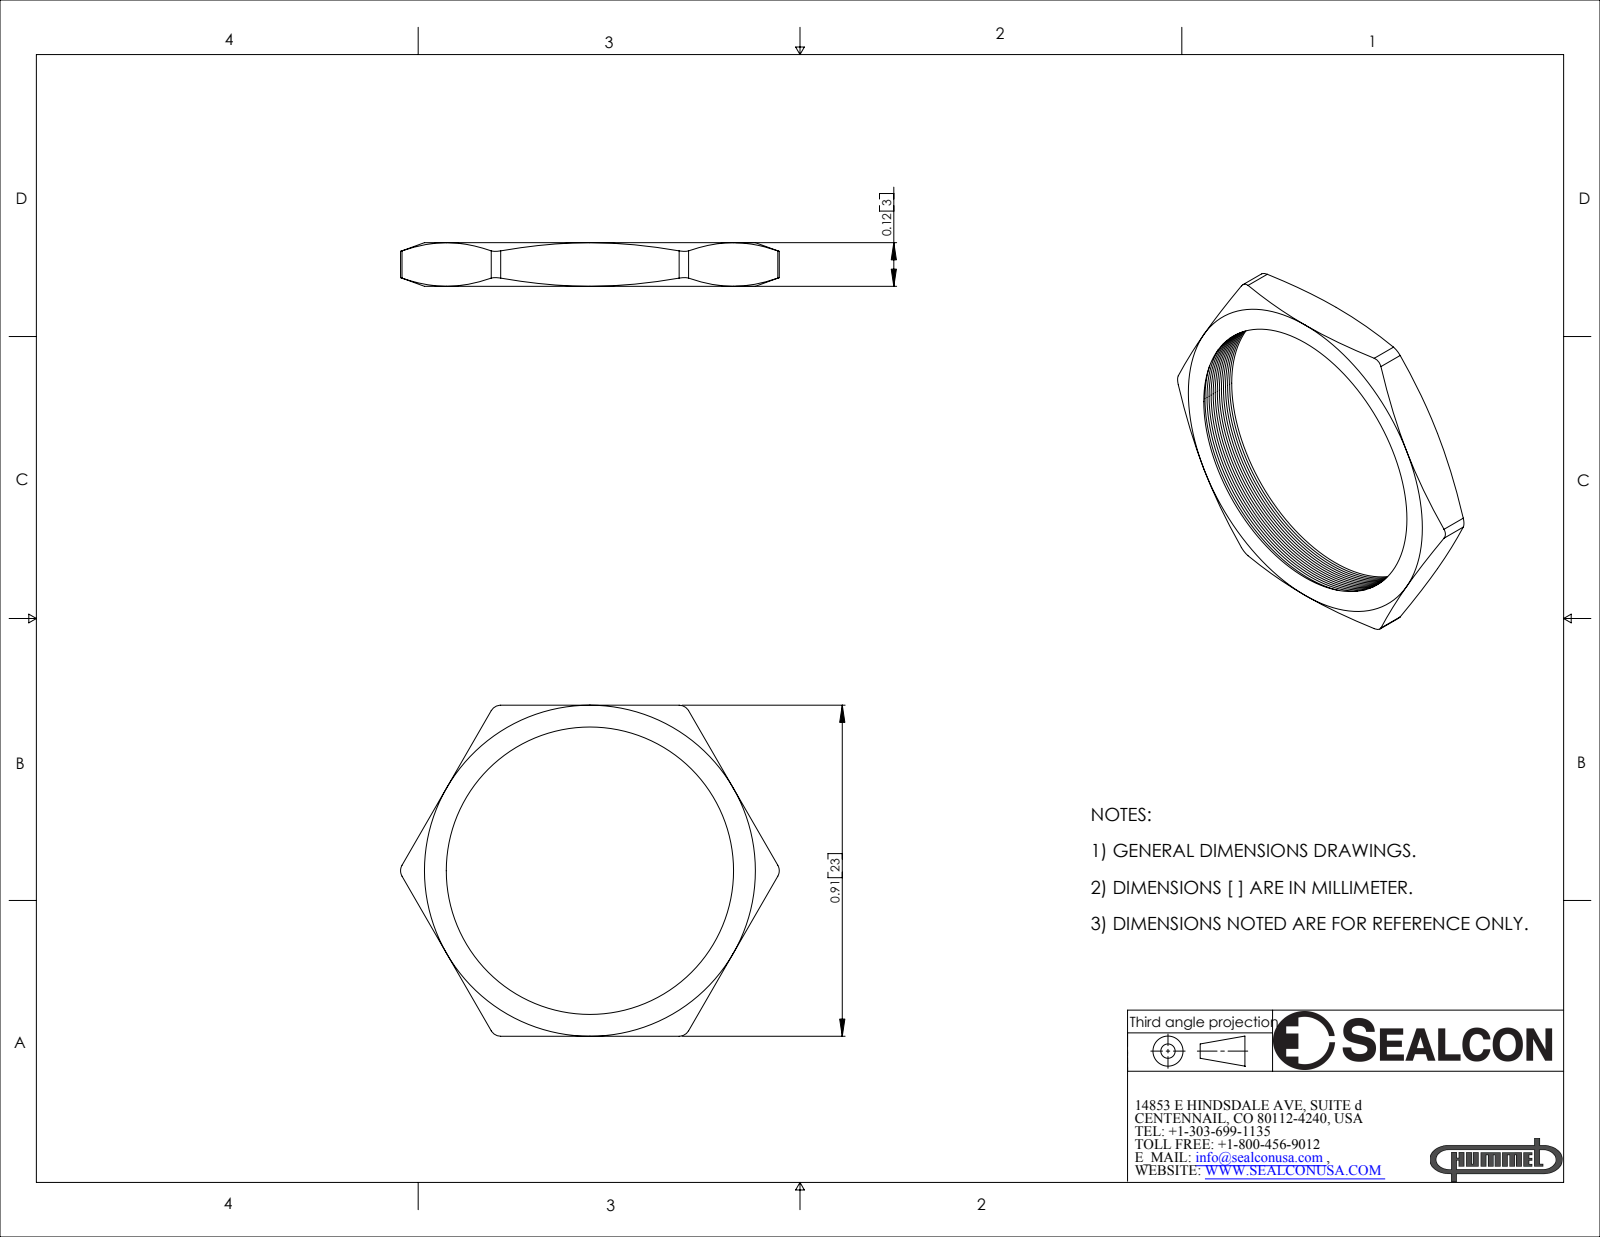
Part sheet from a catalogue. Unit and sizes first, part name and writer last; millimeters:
Units: millimetres
Overall size (bounding box): 26.4 × 23.1 × 3
Partial cylindrical surfaces — rounded edges, fillets, slot ends (radius × count): R0.8 ×6
Main face-to-face distances: 23.1, 3
Volume: 380 mm³ · Surface area: 878 mm²
Bodies: 1 solid, 87 faces (8 planar, 7 cylindrical, 72 other)
Part name (STEP PRODUCT): NM-20-BR
STEP written by: SolidWorks 2007 (CONFIG_CONTROL_DESIGN)
